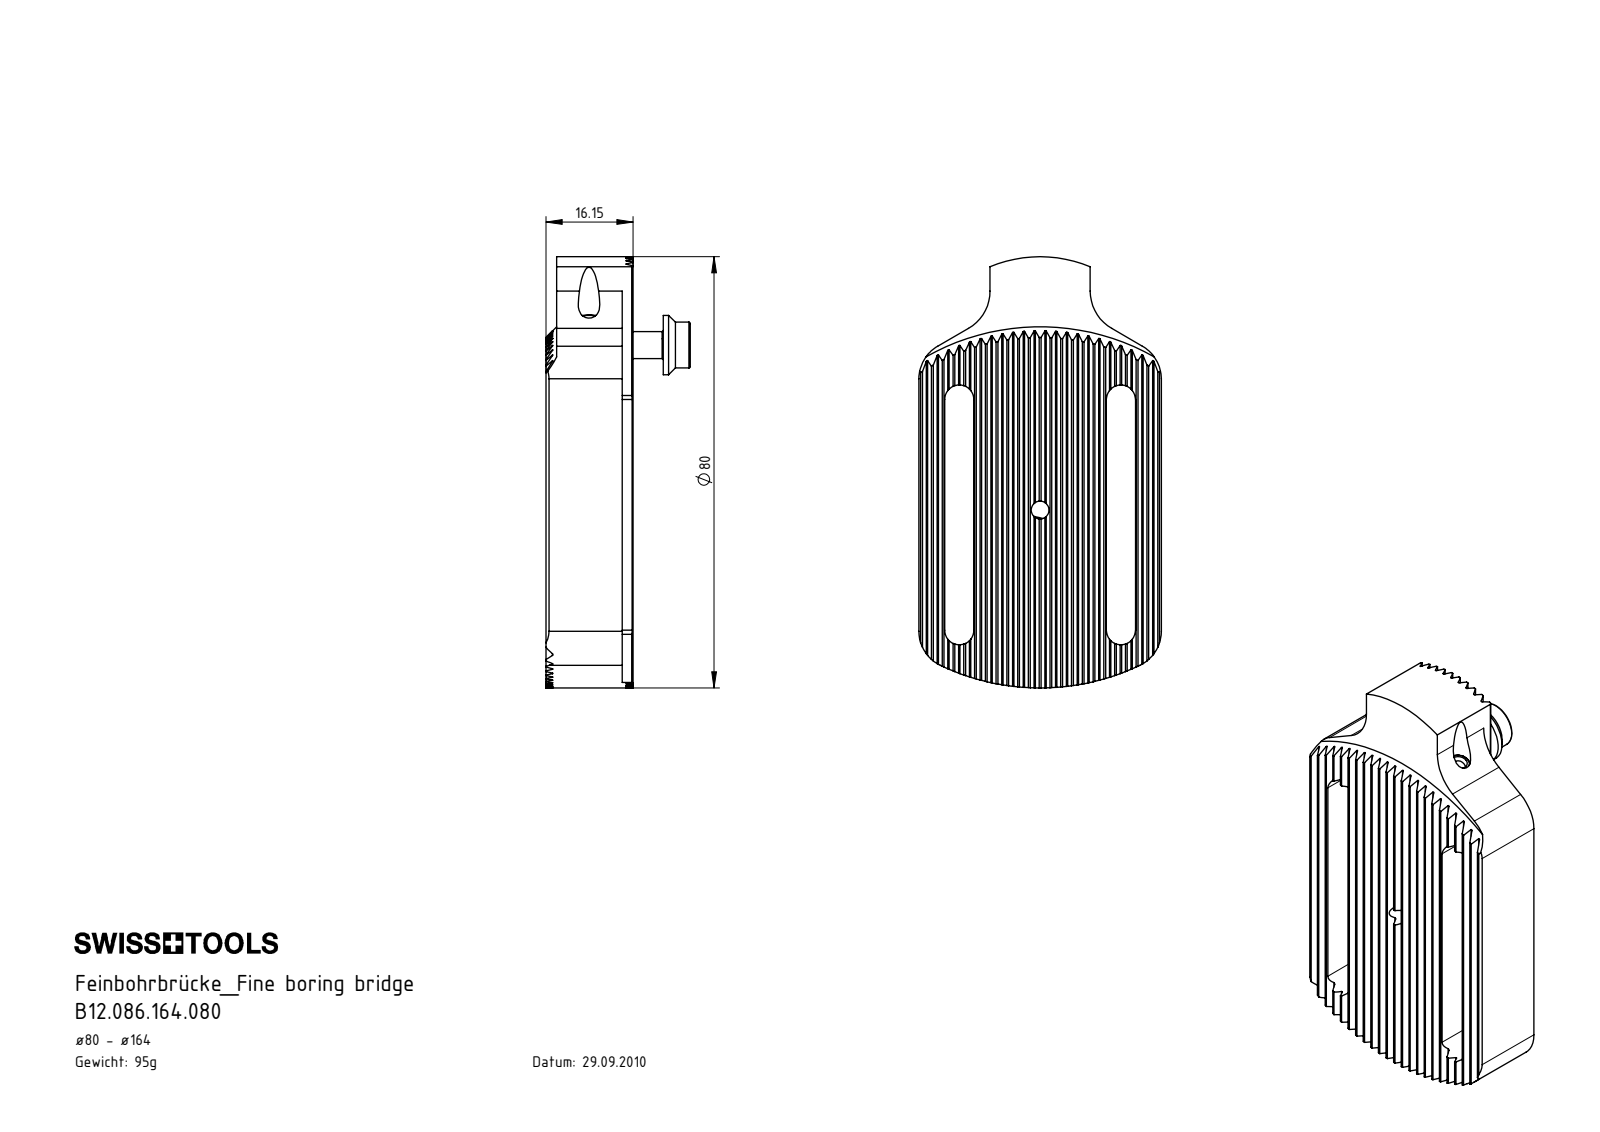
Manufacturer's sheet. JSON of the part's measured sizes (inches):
{"part_name": "B12.086.164.080; MH1-BV2.K01.015_B; KVT_MB_600_040", "step_written_by": "SolidWorks 2017 (CONFIG_CONTROL_DESIGN)", "units": "inches", "bodies": {"solids": 3, "faces": 536, "planar": 325, "cylindrical": 110, "other": 101}, "overall_size": [3.15, 1.772, 0.636], "volume_in3": 1.945, "surface_area_in2": 23.52, "round_holes": [[0.13, 2], [0.165, 2], [0.217, 2], [0.079, 1], [0.118, 1], [0.157, 1]], "round_bosses_or_shafts": [[0.157, 1]], "partial_cylinders_radius": [[0.006, 31], [0.106, 4], [0.226, 4], [0.276, 4], [0.049, 2], [0.315, 2], [0.945, 1], [1.693, 1]], "face_to_face_distances": [0.068, 0.341, 0.136, 0.273, 0.205, 0.227, 0.409, 1.181, 0.12, 0.333], "hole_center_spacings": [0.31, 0.803, 1.098, 1.205, 1.886, 2.008]}
